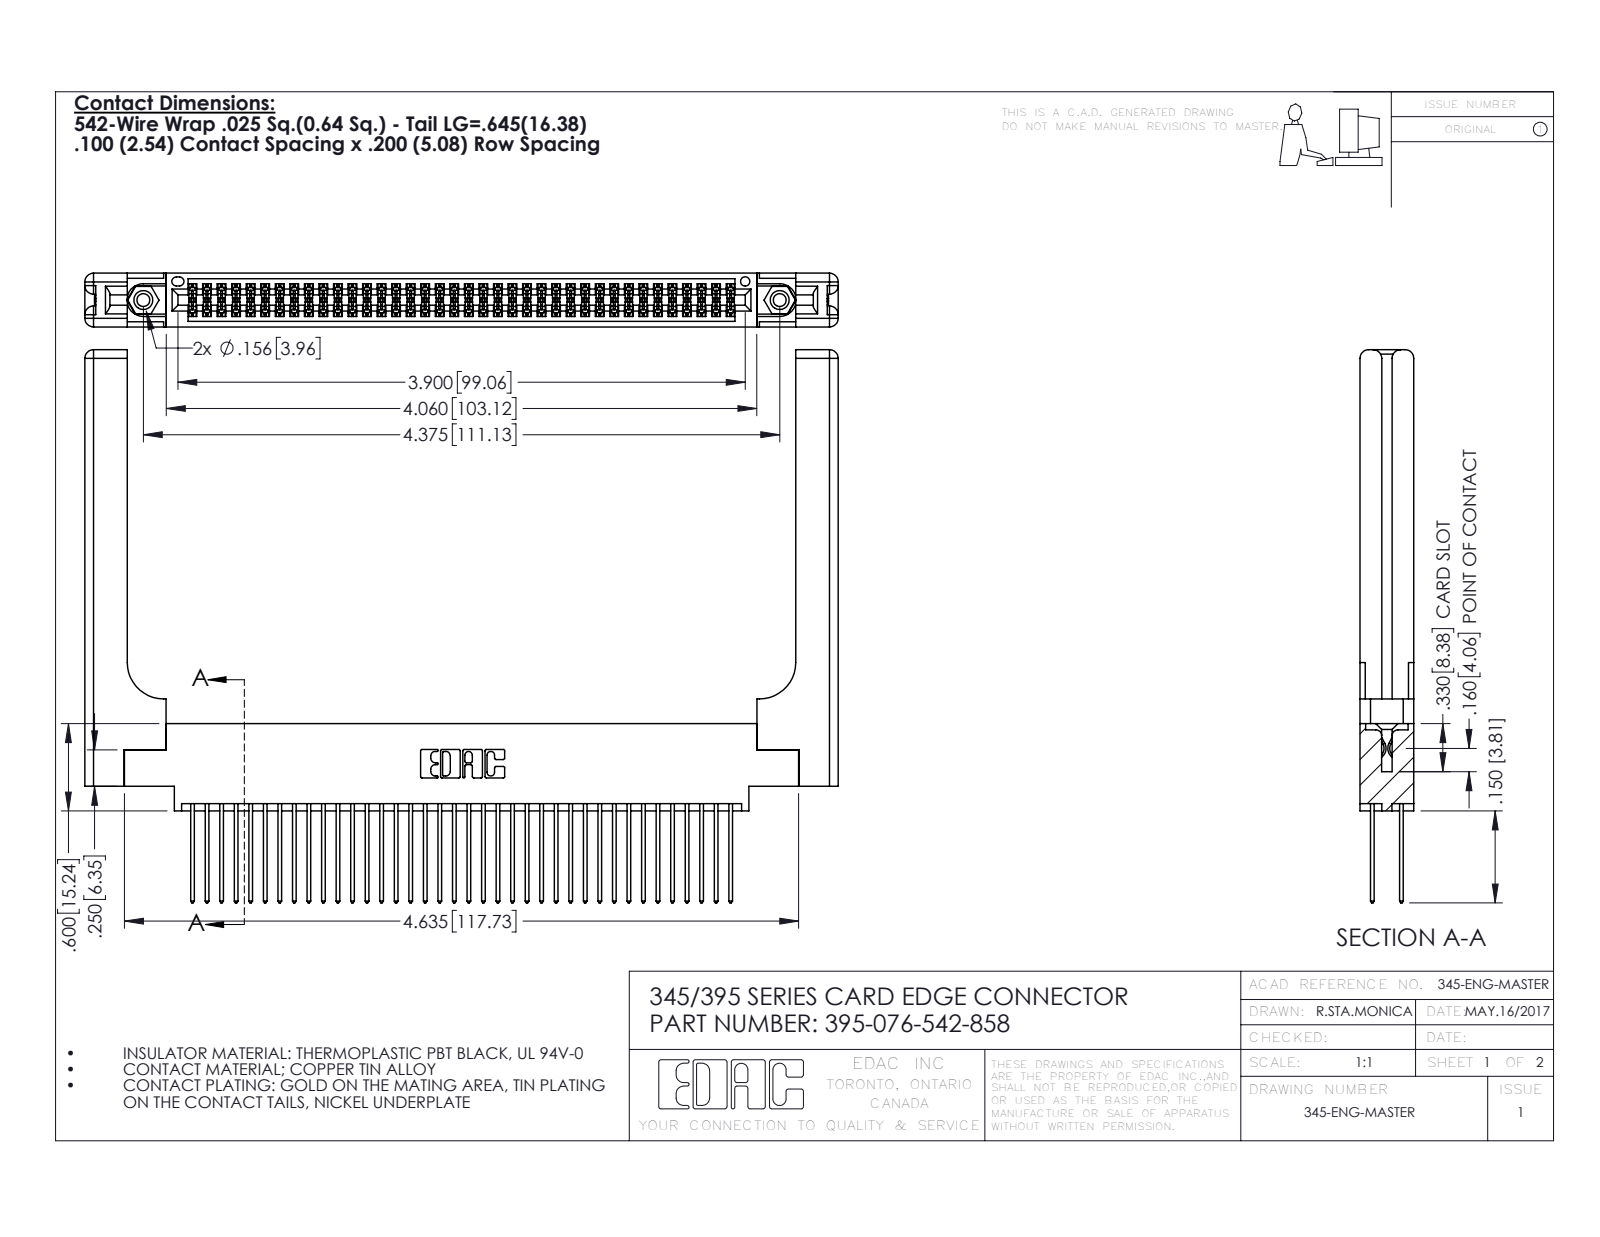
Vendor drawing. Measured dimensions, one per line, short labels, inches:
name: 345 Part_0.170 Offset - 0.156 Dia-TH; 345-250-001_345-250-001-102; 395-076-542-858; 345-292-001_345-293-142 (+1 more)
written by: SolidWorks 2016 (CONFIG_CONTROL_DESIGN)
unit: in
bodies: 81 solids, 4186 faces (2740 planar, 1386 cylindrical, 60 other)
size: 5.179 × 3.802 × 0.37
volume: 1.309 in³; area: 40.25 in²
holes: 2× ⌀0.089, 2× ⌀0.125, 2× ⌀0.156, 1× ⌀0.064
bosses: 2× ⌀0.155
rounds: 114× R0.006, 76× R0.01, 22× R0.01, 16× R0.06, 6× R0.007, 6× R0.031, 3× R0.026, 2× R0.014
face distances: 0.072, 0.298, 0.37, 0.098, 0.272, 0.025, 0.2, 0.225, 0.175, 0.148
hole spacings: 0.27, 4.139, 4.375
